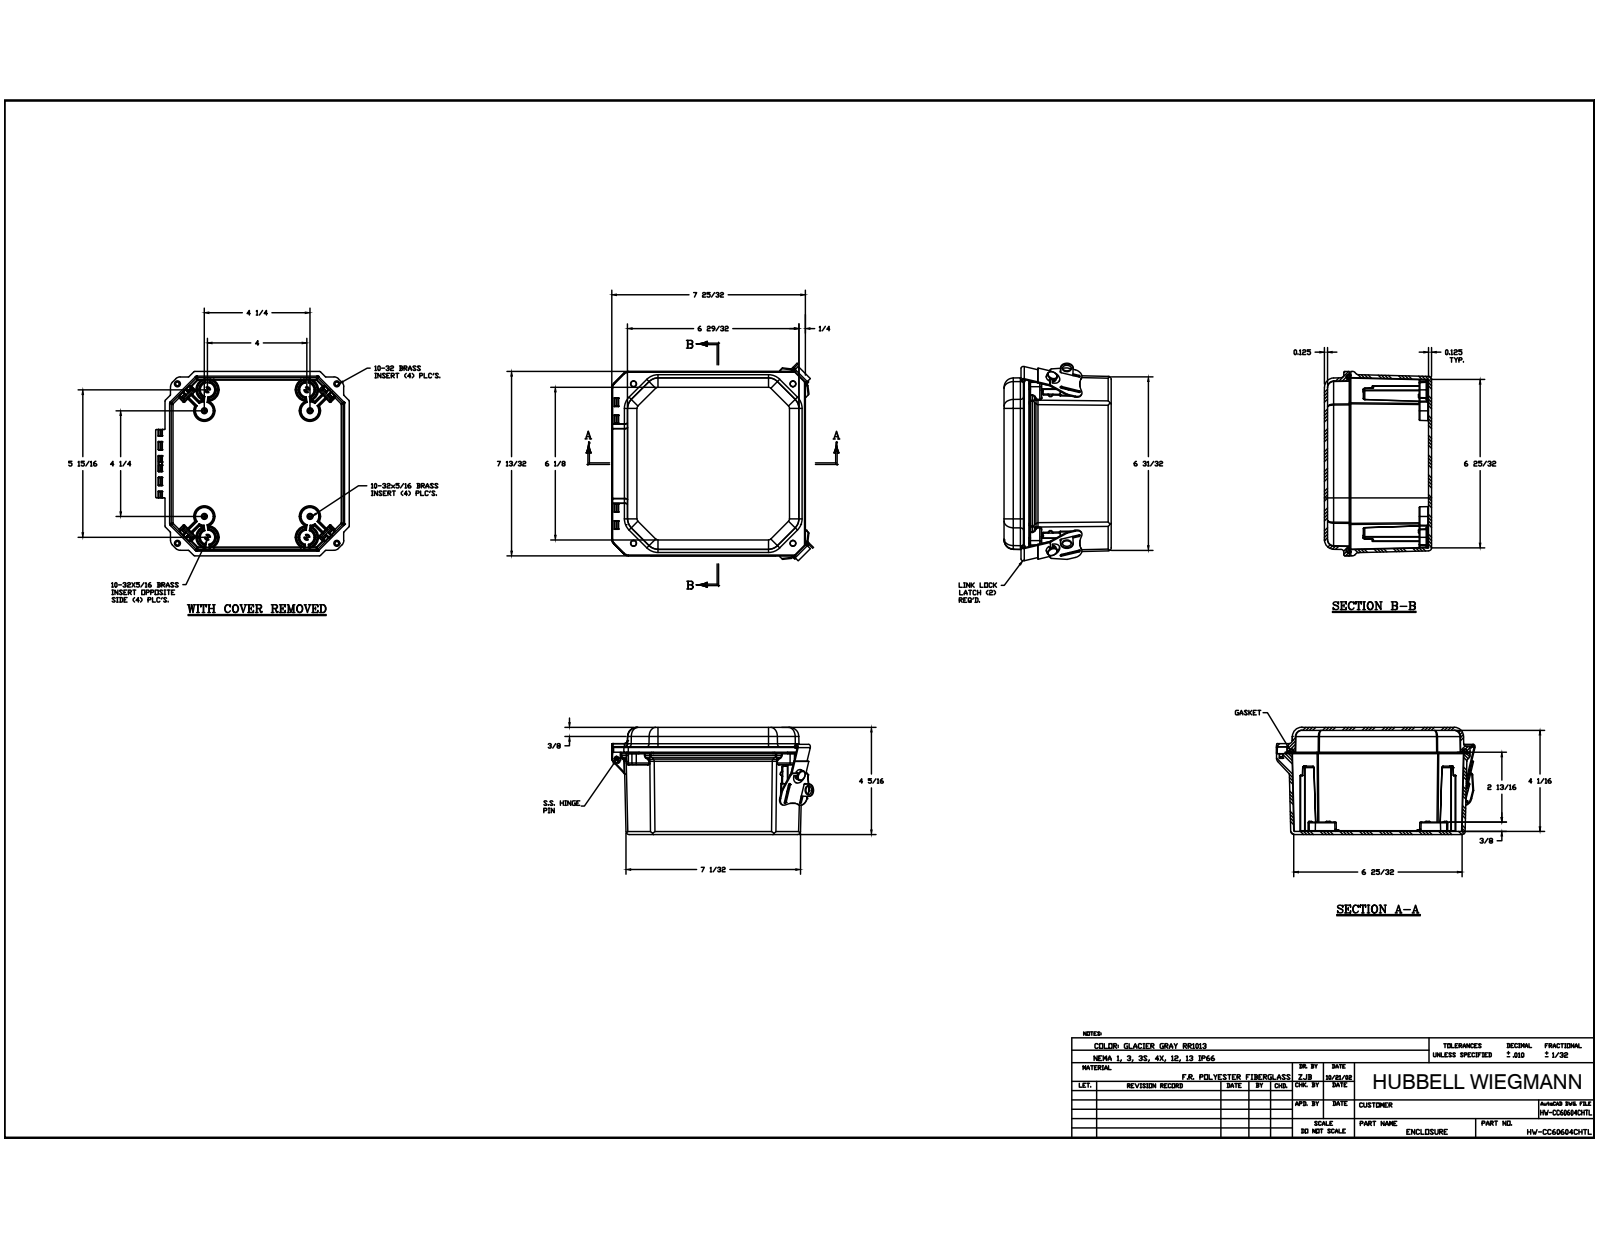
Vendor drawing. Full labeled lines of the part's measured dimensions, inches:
Part name (STEP PRODUCT): DS060604BOX; DSCC060604CVR; GA606; WP606HLU (+6 more)
STEP written by: Autodesk Inventor 2014 (AUTOMOTIVE_DESIGN)
Units: inches
Bodies: 33 solids, 2207 faces (648 planar, 845 cylindrical, 714 other)
Overall size (bounding box): 8.261 × 8.214 × 4.312
Volume: 32.71 in³ · Surface area: 511.6 in²
Round holes (diameter × count): ⌀0.156 ×12, ⌀0.152 ×8, ⌀0.15 ×4, ⌀0.219 ×4, ⌀0.252 ×4, ⌀0.312 ×4, ⌀0.05 ×2, ⌀0.098 ×2, ⌀0.12 ×2, ⌀0.363 ×2, ⌀0.137 ×1
Round bosses / shafts (diameter × count): ⌀0.246 ×12, ⌀0.87 ×4, ⌀0.209 ×4, ⌀0.135 ×3, ⌀0.6 ×2, ⌀0.2 ×2, ⌀0.05 ×2
Partial cylindrical surfaces — rounded edges, fillets, slot ends (radius × count): R0.01 ×156, R0.005 ×96, R0.02 ×65, R0.125 ×41, R0.03 ×38, R0.039 ×28, R0.25 ×26, R0.03 ×24
Main face-to-face distances: 0.125, 4.187, 4.312, 4.062, 0.124, 0.125, 3.531, 0.656, 0.375, 1
Hole centre spacings: 5.441, 6.414, 4.25, 4.25, 5.441, 6.289, 7.541, 0.849
